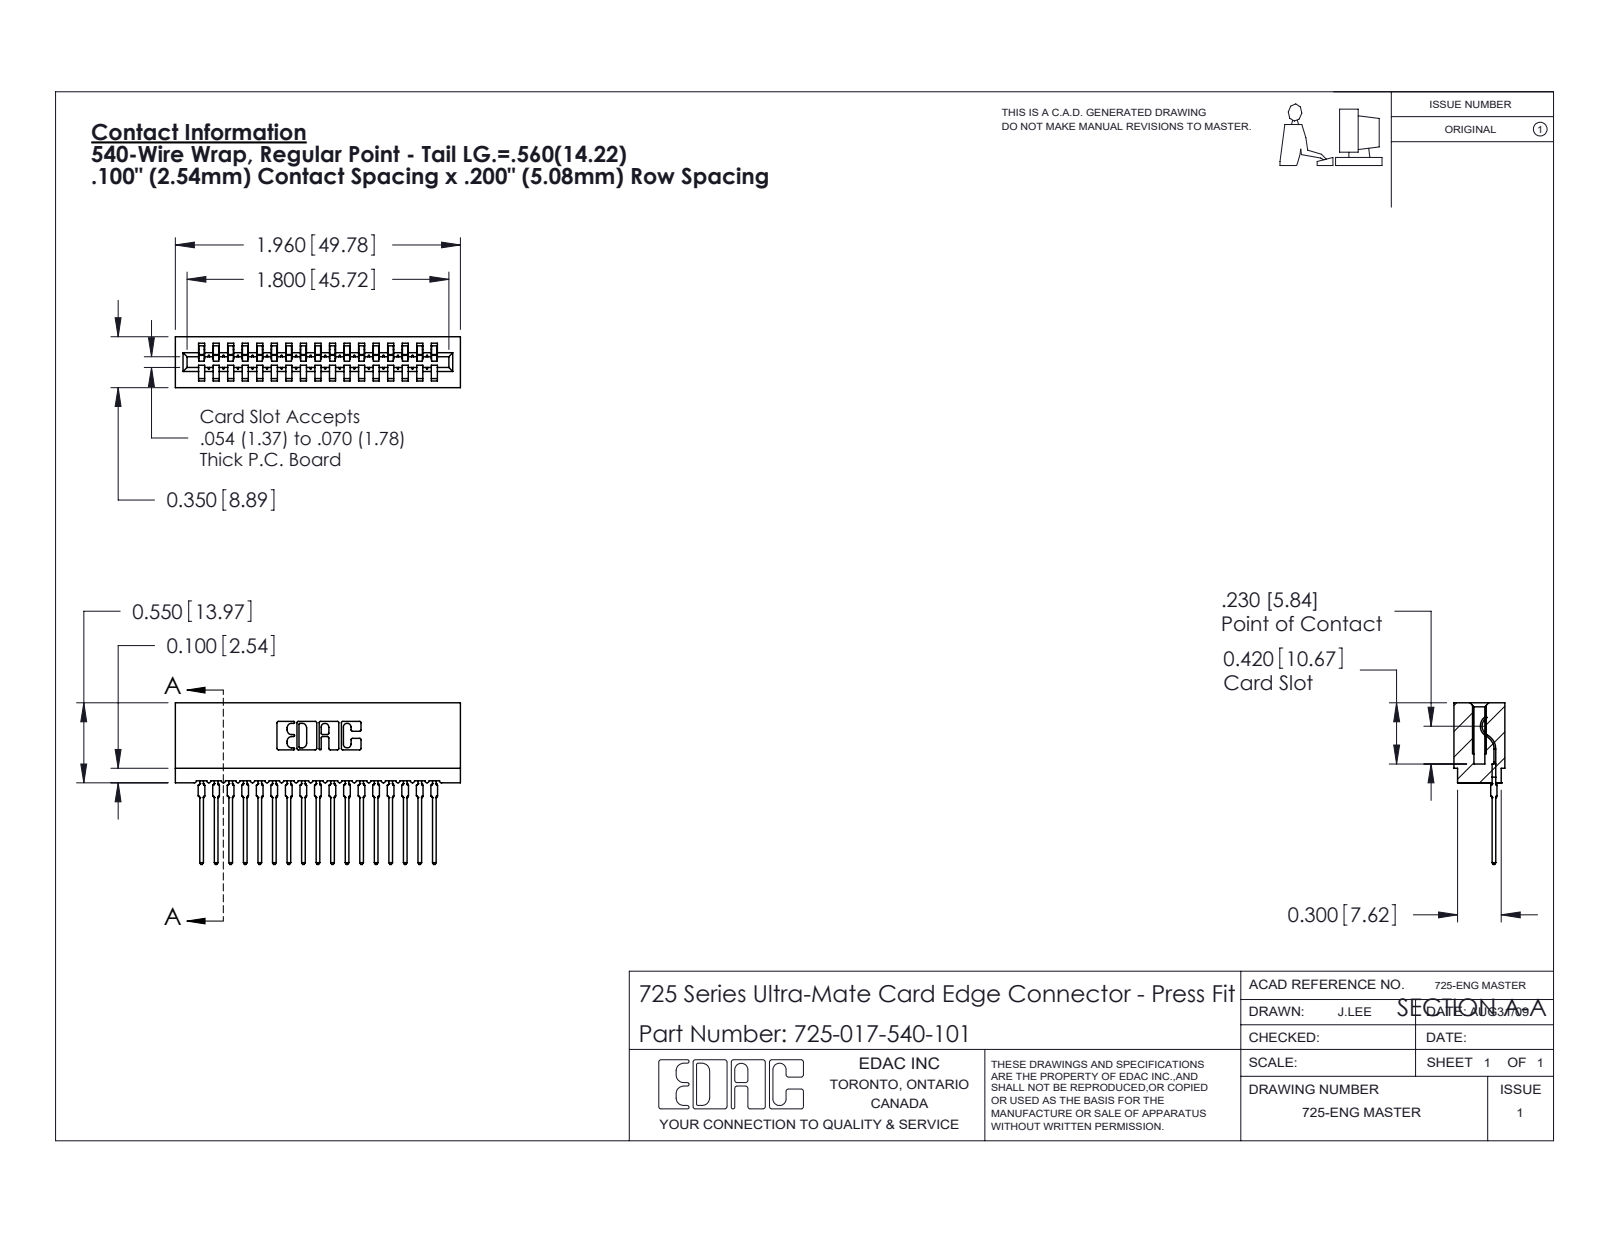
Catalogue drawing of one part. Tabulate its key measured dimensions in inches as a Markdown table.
| quantity | value |
| --- | --- |
| part name | 725 Part_Insulator Option - 01; 745-292-001_540; 725-017-540-101 |
| STEP written by | SolidWorks 2020 (CONFIG_CONTROL_DESIGN) |
| units | inches |
| bodies | 18 solids, 1999 faces (1194 planar, 363 cylindrical, 442 other) |
| overall size | 1.96 × 1.111 × 0.35 |
| volume | 0.242 in³ |
| surface area | 11.39 in² |
| partial cylindrical surfaces (radius × count) | 0.015 × 34, 0.021 × 34, 0.01 × 22, 0.007 × 6, 0.031 × 6, 0.005 × 4, 0.011 × 4, 0.026 × 3 |
| main face-to-face distances | 0.1, 0.2, 0.3, 0.4, 0.5, 0.6, 0.7, 0.35, 0.8, 0.212 |
